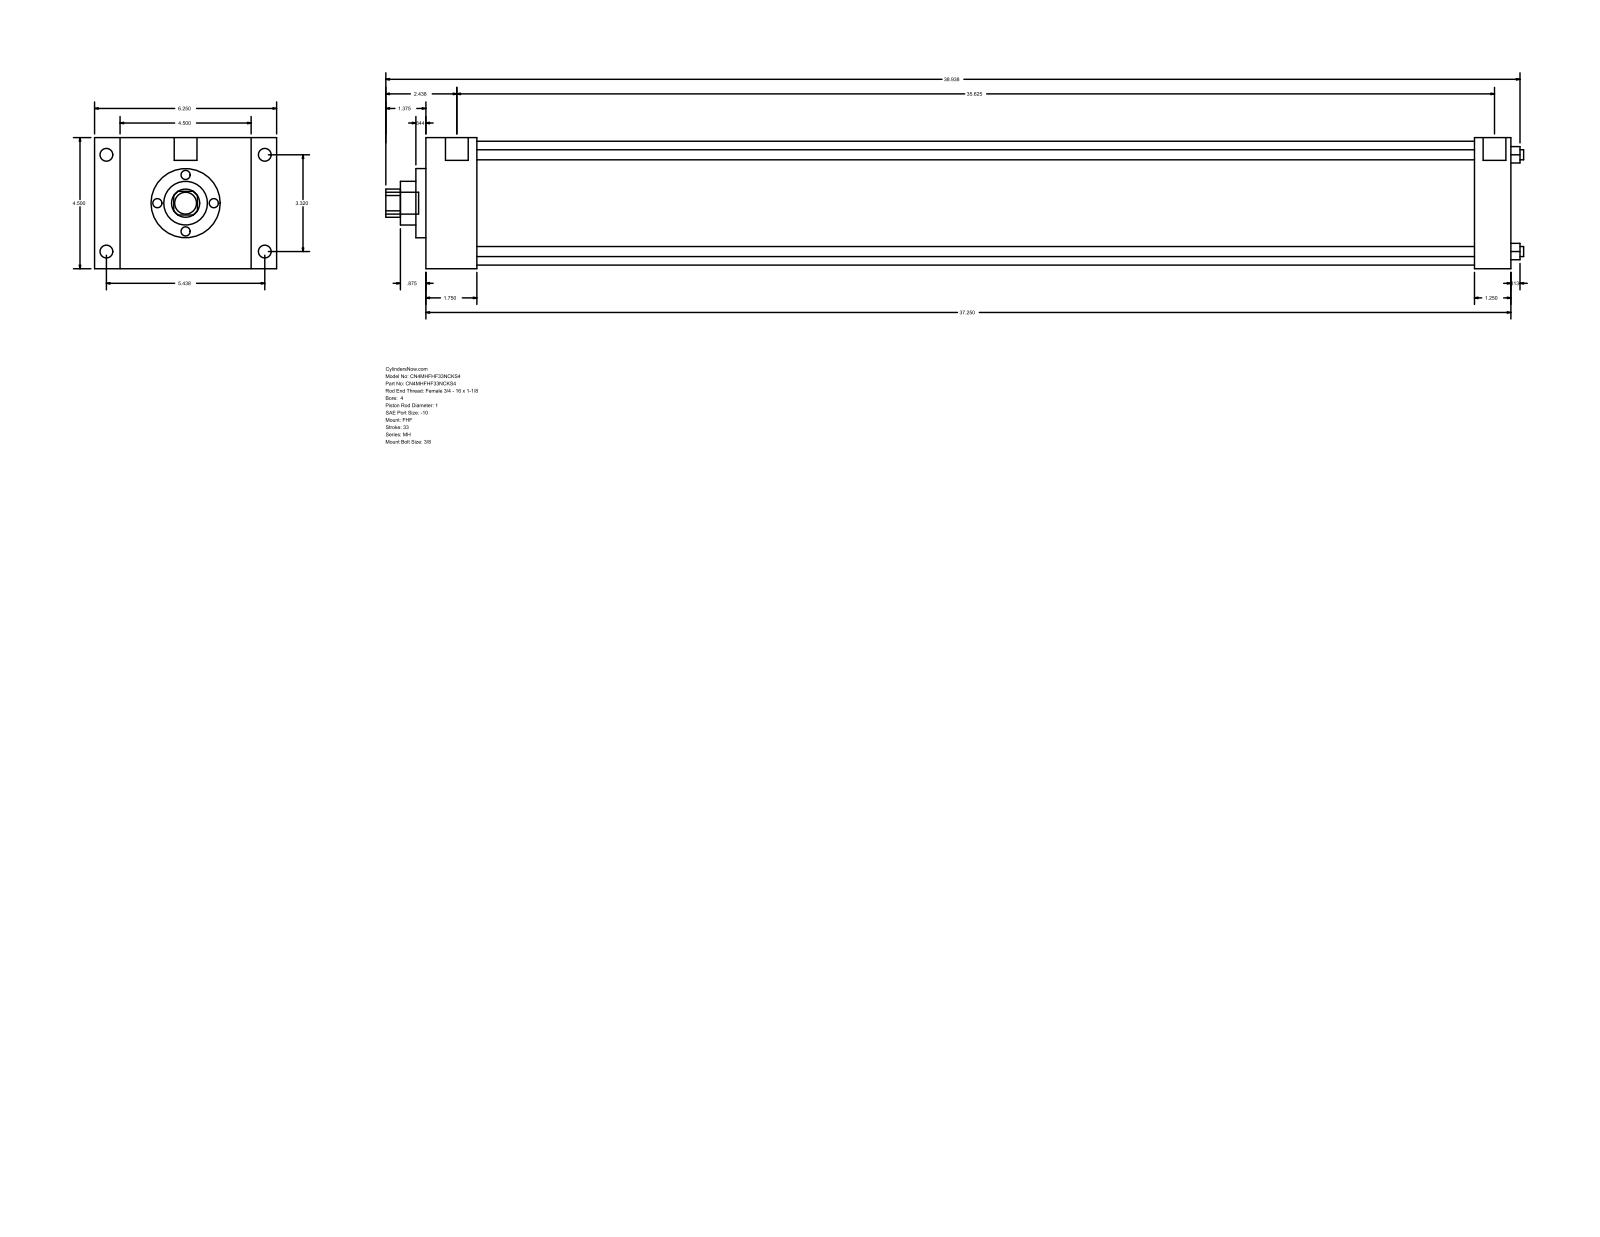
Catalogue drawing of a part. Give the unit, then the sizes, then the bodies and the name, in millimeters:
Units: millimetres
Overall size (bounding box): 992.19 × 158.75 × 114.3
Round holes (diameter × count): ⌀8.76 ×4, ⌀25.4 ×1, ⌀38.1 ×1, ⌀60.33 ×1, ⌀107.95 ×1
Round bosses / shafts (diameter × count): ⌀11.13 ×4, ⌀8.73 ×4, ⌀19.84 ×2, ⌀19.05 ×1
Partial cylindrical surfaces — rounded edges, fillets, slot ends (radius × count): R12.29 ×1
Main face-to-face distances: 114.3, 946.16, 44.46, 901.7, 22.23, 136.53, 158.76, 914.41, 869.95, 31.75
Hole centre spacings: 59.62, 84.32, 119.25
Bodies: 0 solids, 90 faces (61 planar, 29 cylindrical, 0 other)
Part name (STEP PRODUCT): MH_FHF__0400_1
STEP written by: GSSL Pune (CONFIG_CONTROL_DESIGN)
